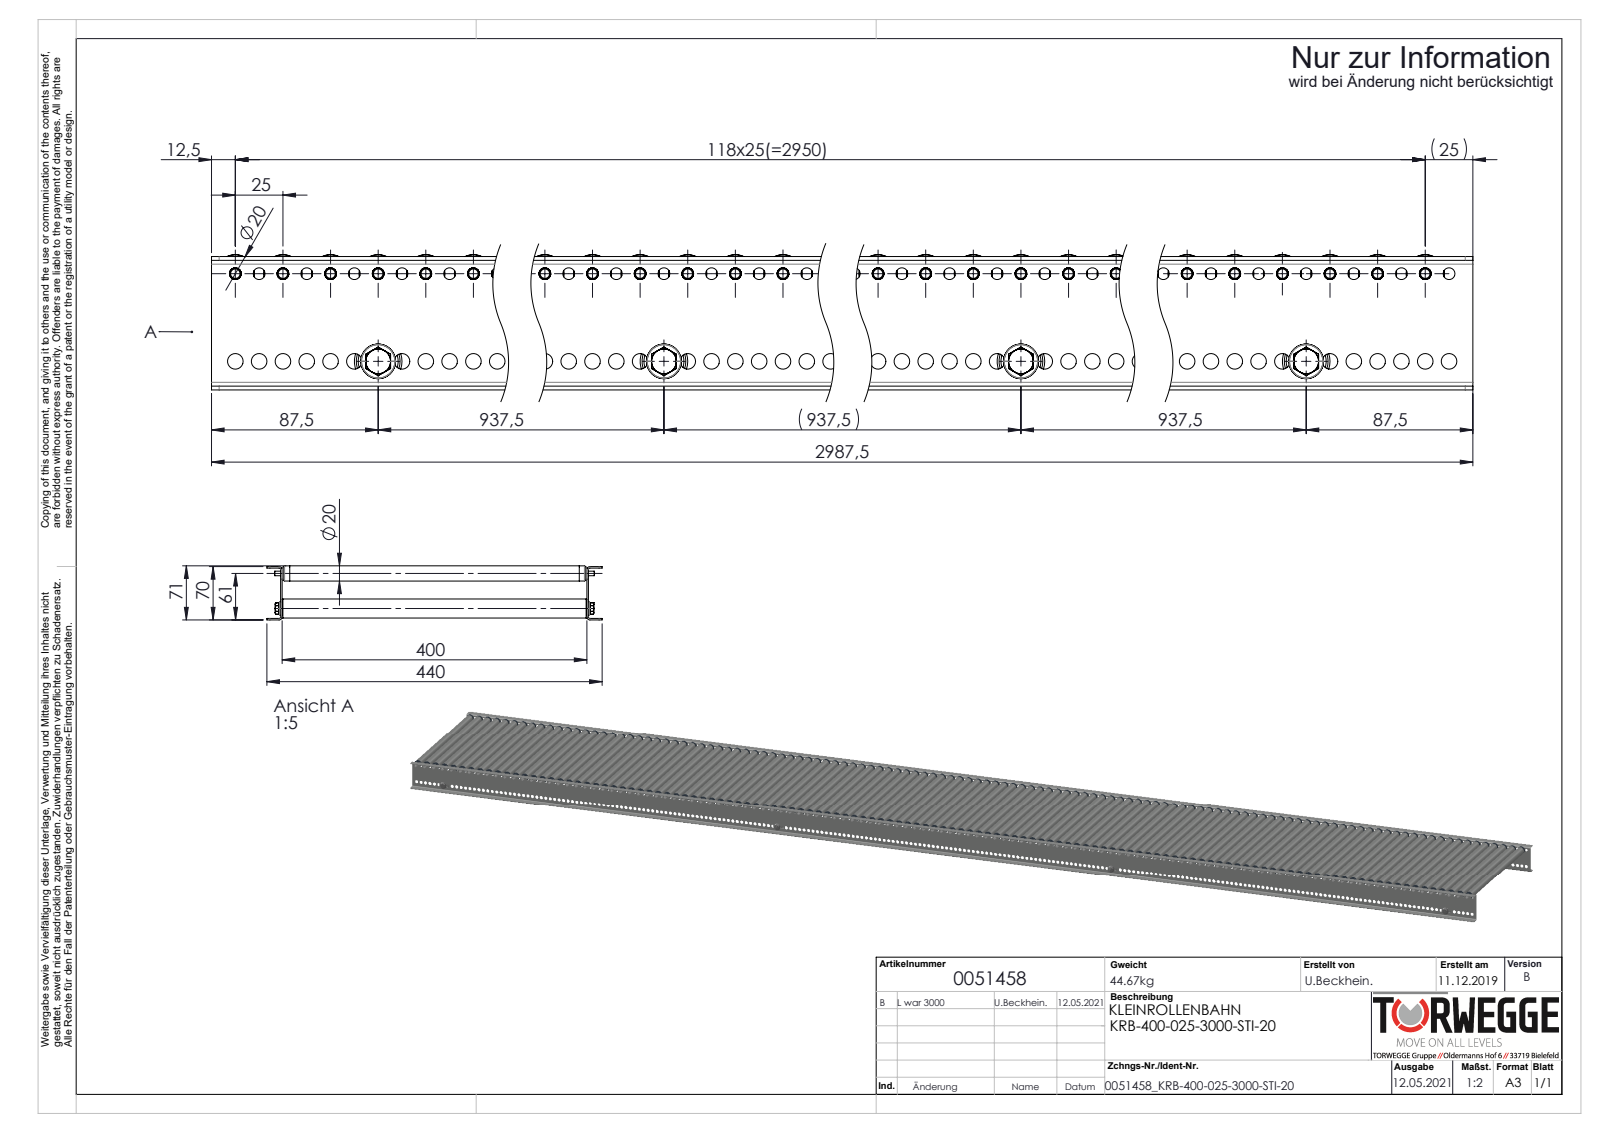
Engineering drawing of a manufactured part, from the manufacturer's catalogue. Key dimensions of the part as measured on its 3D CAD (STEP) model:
Part name (STEP PRODUCT): Traversen_KFG_L400; S100993_Tragrollenrohr-Ø20x1STI_KFG_L=380; Profil_KRB-20x70x20x2_KFG_S109089_U-PROFIL-20-70-20-2-KRB-20-L=2987,5; KUT50-20x1,5-STI-A6_FA-EL=KFG_S100910_KUT50-20x1-STI-A6-FA-EL=400 (+4 more)
STEP written by: SolidWorks 2020 (AUTOMOTIVE_DESIGN)
Units: millimetres
Bodies: 260 solids, 23356 faces (7582 planar, 8902 cylindrical, 6872 other)
Overall size (bounding box): 2987.5 × 440 × 71
Volume: 5 556 000 mm³ · Surface area: 8 602 000 mm²
Round holes (diameter × count): ⌀6.2 ×238, ⌀8.2 ×238, ⌀6.1 ×119, ⌀14.2 ×119, ⌀17.2 ×119, ⌀18 ×119, ⌀6.8 ×4, ⌀21 ×4
Round bosses / shafts (diameter × count): ⌀20 ×119, ⌀19.9 ×119, ⌀18.1 ×119, ⌀17.8 ×119, ⌀16.5 ×119, ⌀6 ×119, ⌀25 ×4, ⌀8 ×4
Partial cylindrical surfaces — rounded edges, fillets, slot ends (radius × count): R4.05 ×119, R4 ×8, R2 ×4
Main face-to-face distances: 2, 402, 68, 400, 404, 70, 66, 392, 18, 30
Hole centre spacings: 12.5, 25, 37.5, 50, 62.5, 75, 87.5, 100
